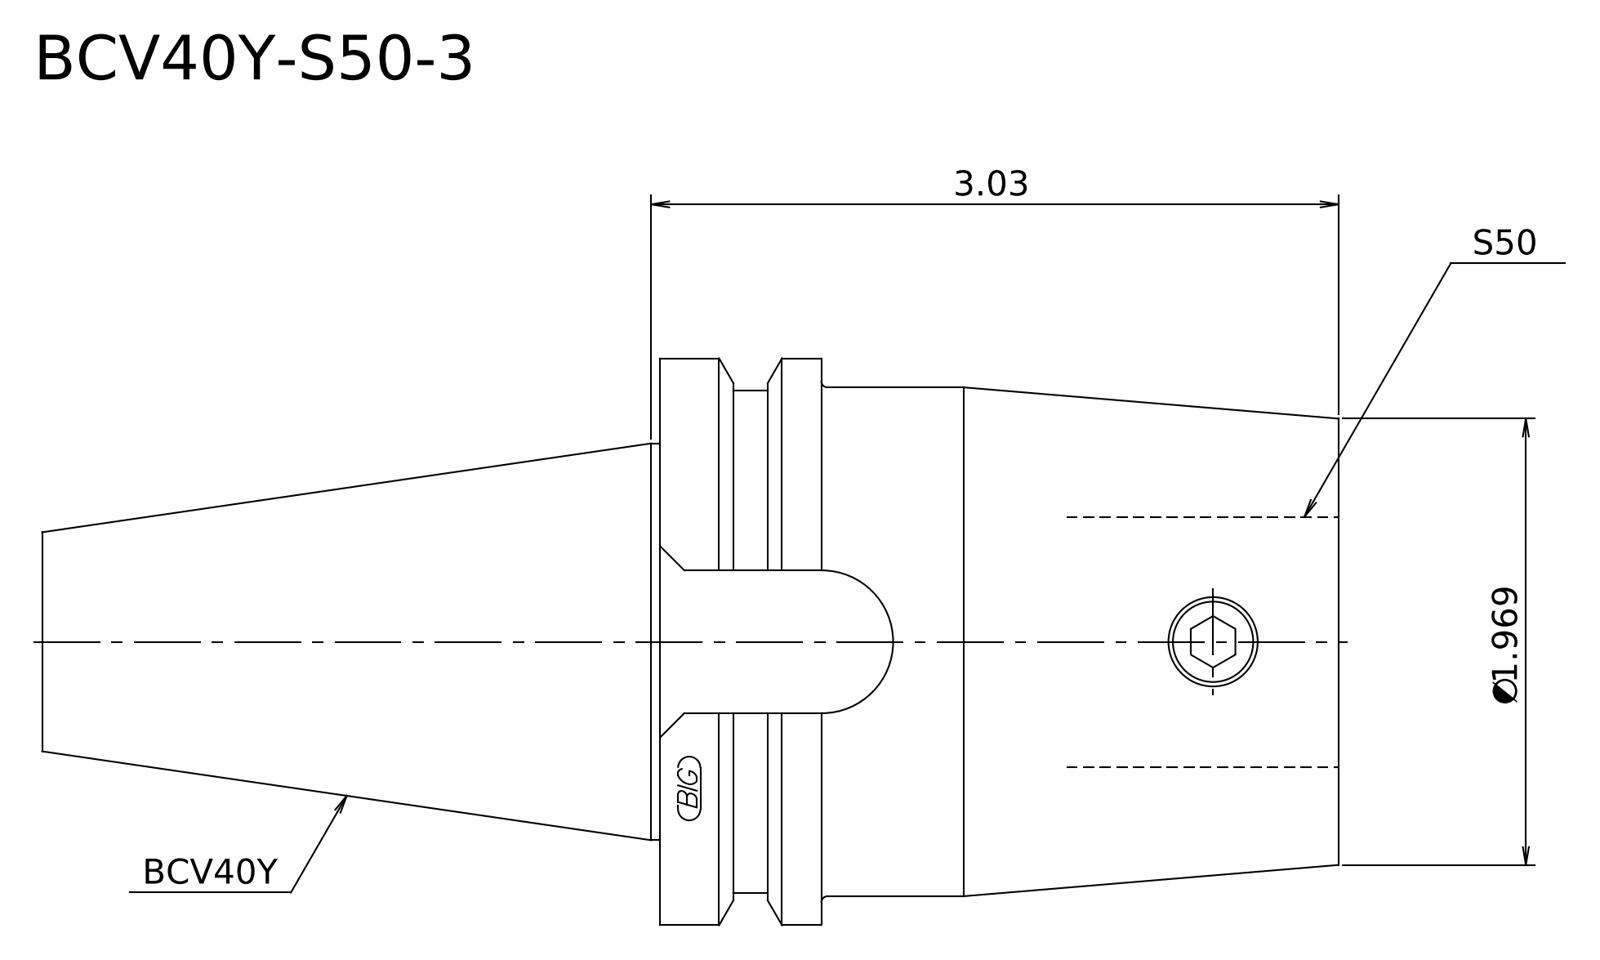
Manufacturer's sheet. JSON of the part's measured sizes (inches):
{"step_written_by": "Kubotek KeyCreator 2011 V10.0.2 (22737) (automotive_design)", "units": "inches", "bodies": {"solids": 1, "faces": 16, "planar": 6, "cylindrical": 5, "other": 5}, "overall_size": [5.719, 2.5, 2.5], "volume_in3": 15.63, "surface_area_in2": 41.12, "round_bosses_or_shafts": [[2.5, 1], [2.244, 1], [2.219, 1], [1.75, 1]], "face_to_face_distances": [2.992, 2.281, 0.711, 5.719, 3.437, 2.726, 2.518, 0.237, 0.474, 3.2]}
